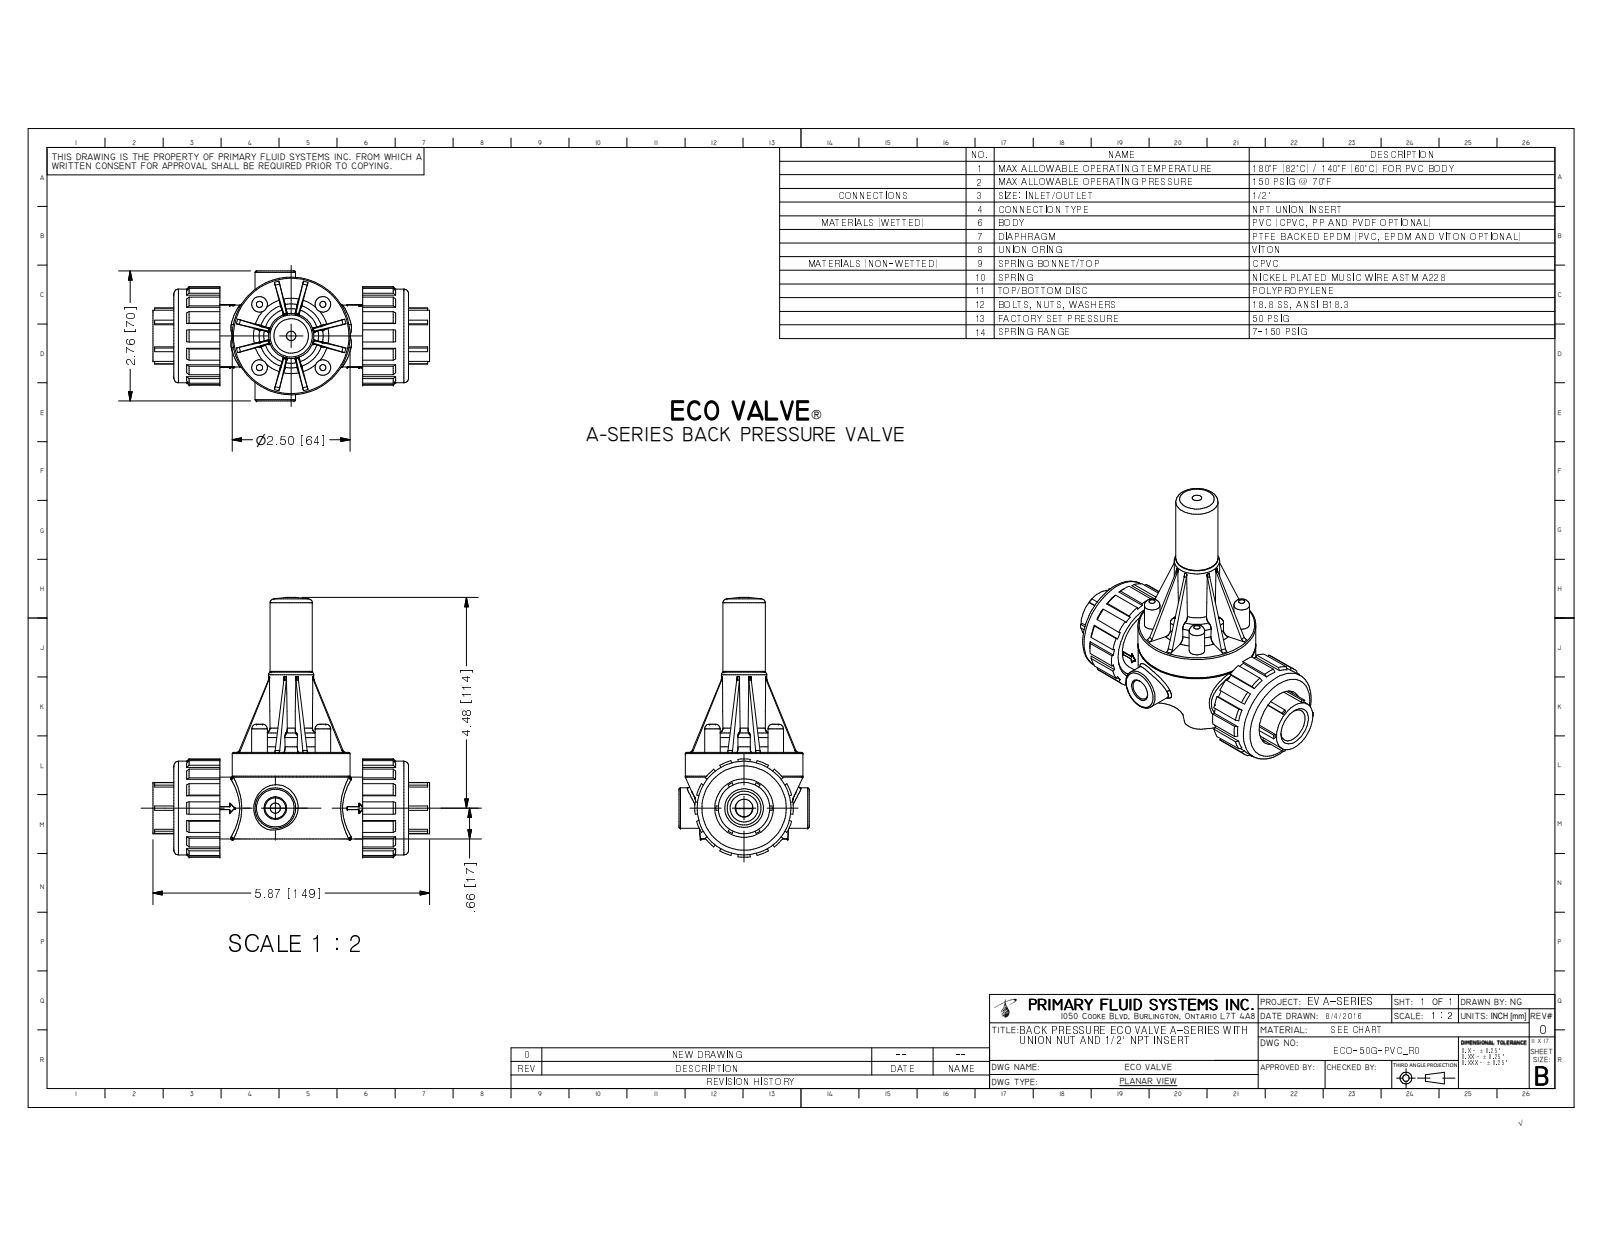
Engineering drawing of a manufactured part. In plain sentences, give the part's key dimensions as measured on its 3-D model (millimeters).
The part is named "ECO-50G-PVC_R0". Its 3-D file was written by "Autodesk Inventor 2009 (AUTOMOTIVE_DESIGN)". It is 1 solid with 851 faces: 264 planar, 182 cylindrical and 405 other. Overall it measures 149 by 140.2 by 70.2 millimeters. Its volume is 484 200 cubic millimeters and its surface area 35 460 square millimeters. Round holes: 4 of diameter 6.5, 1 of diameter 11.1, 1 of diameter 18.3, 1 of diameter 19.5, 1 of diameter 29.9, 1 of diameter 33.4, 1 of diameter 38.2, 1 of diameter 42.9. Round bosses or shafts: 4 of diameter 10.2, 4 of diameter 8.4, 4 of diameter 6.5, 4 of diameter 5.8, 1 of diameter 63.5, 1 of diameter 35, 1 of diameter 34.5, 1 of diameter 27.7. Partial cylindrical surfaces (rounded edges, fillets, slot ends): 8 of radius 1.8, 8 of radius 2.5, 4 of radius 3.3, 4 of radius 6.5, 4 of radius 7.4, 1 of radius 12.9, 1 of radius 15.1, 1 of radius 16.9. The main face-to-face distances are 46.7, 106.7, 21.2, 127.8, 19.6, 129.4, 1.5, 108.2, 23.4, 125.6. The hole center spacings are 34.1, 34.1, 48.3.
